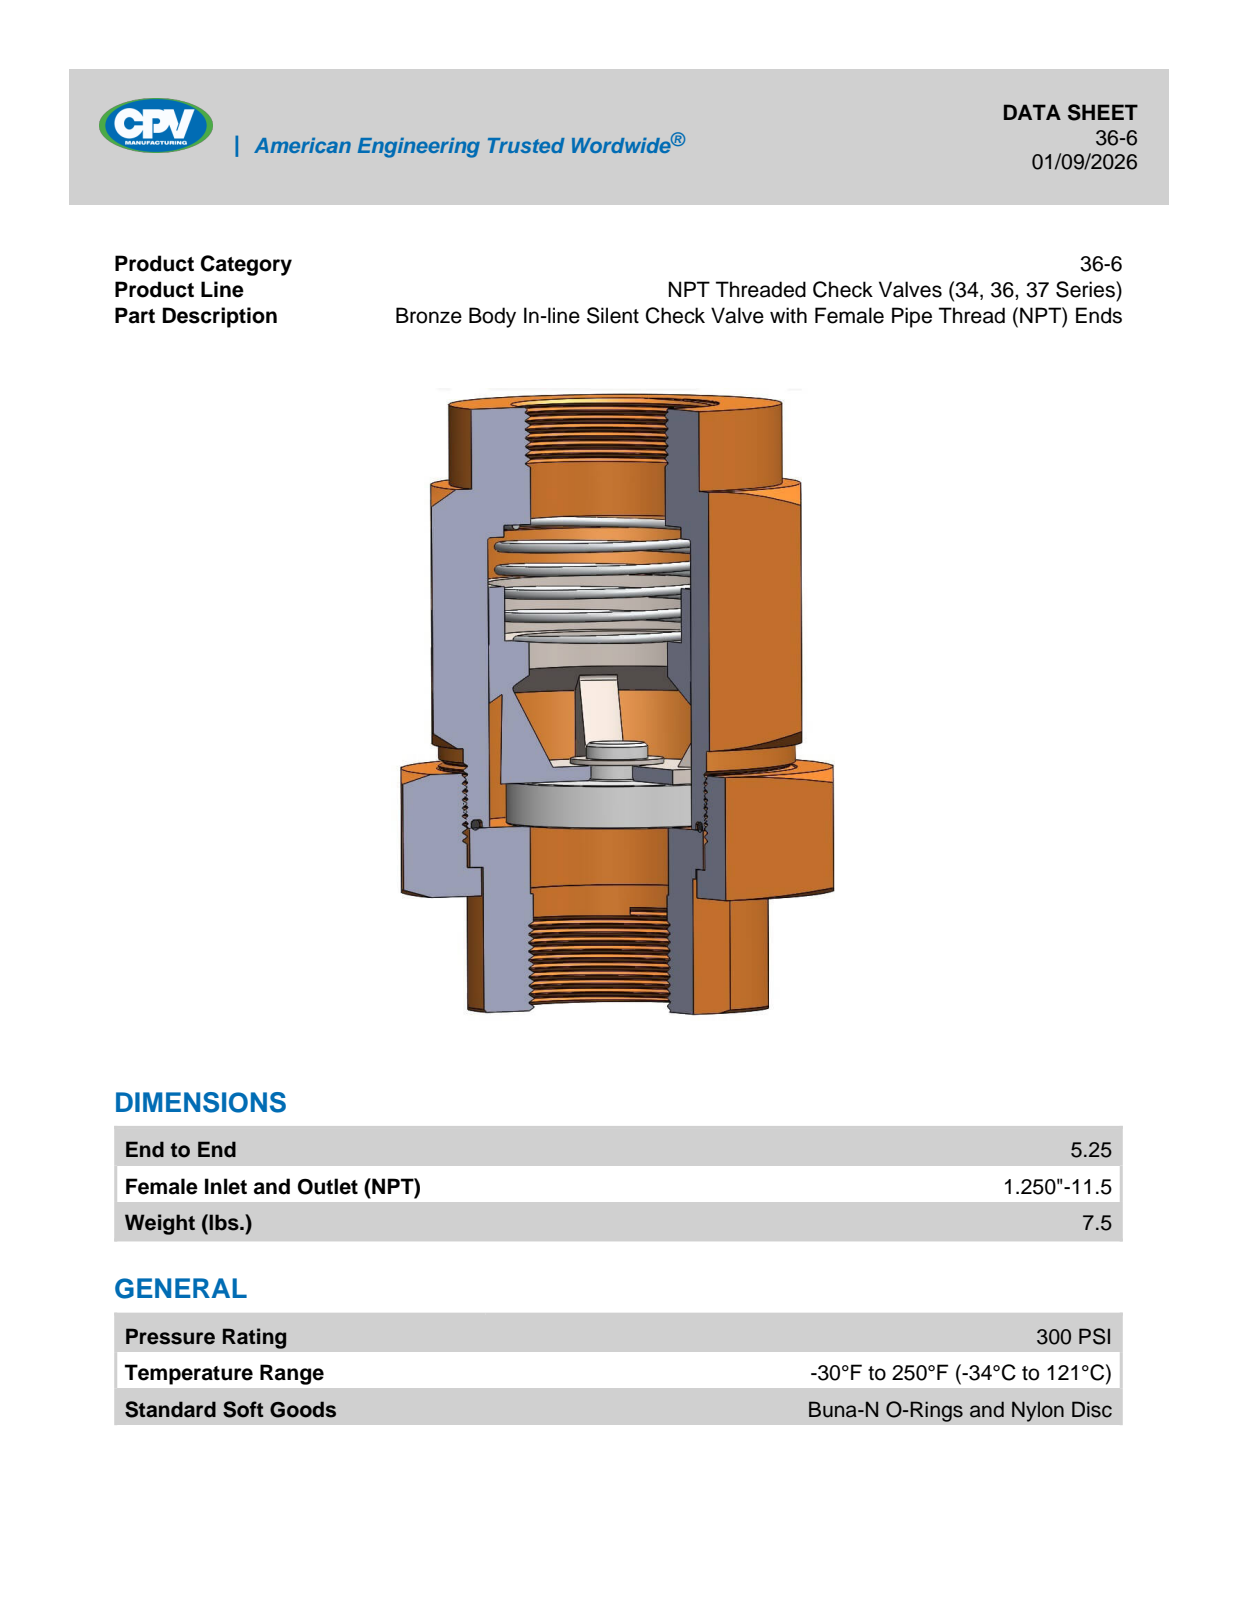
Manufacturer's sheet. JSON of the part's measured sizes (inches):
{"part_name": "36-6", "step_written_by": "SolidWorks 2018 (AUTOMOTIVE_DESIGN)", "units": "inches", "bodies": {"solids": 1, "faces": 108, "planar": 28, "cylindrical": 39, "other": 41}, "overall_size": [5.19, 3.903, 3.38], "volume_in3": 31.59, "surface_area_in2": 82.41, "round_holes": [[1.25, 1]], "round_bosses_or_shafts": [[2.745, 1], [2.5, 1]], "partial_cylinders_radius": [[1.155, 1]], "face_to_face_distances": [2.88, 0.25, 3.13, 0.345, 2.535, 0.25, 3.13, 3.38, 4.02, 0.595]}
